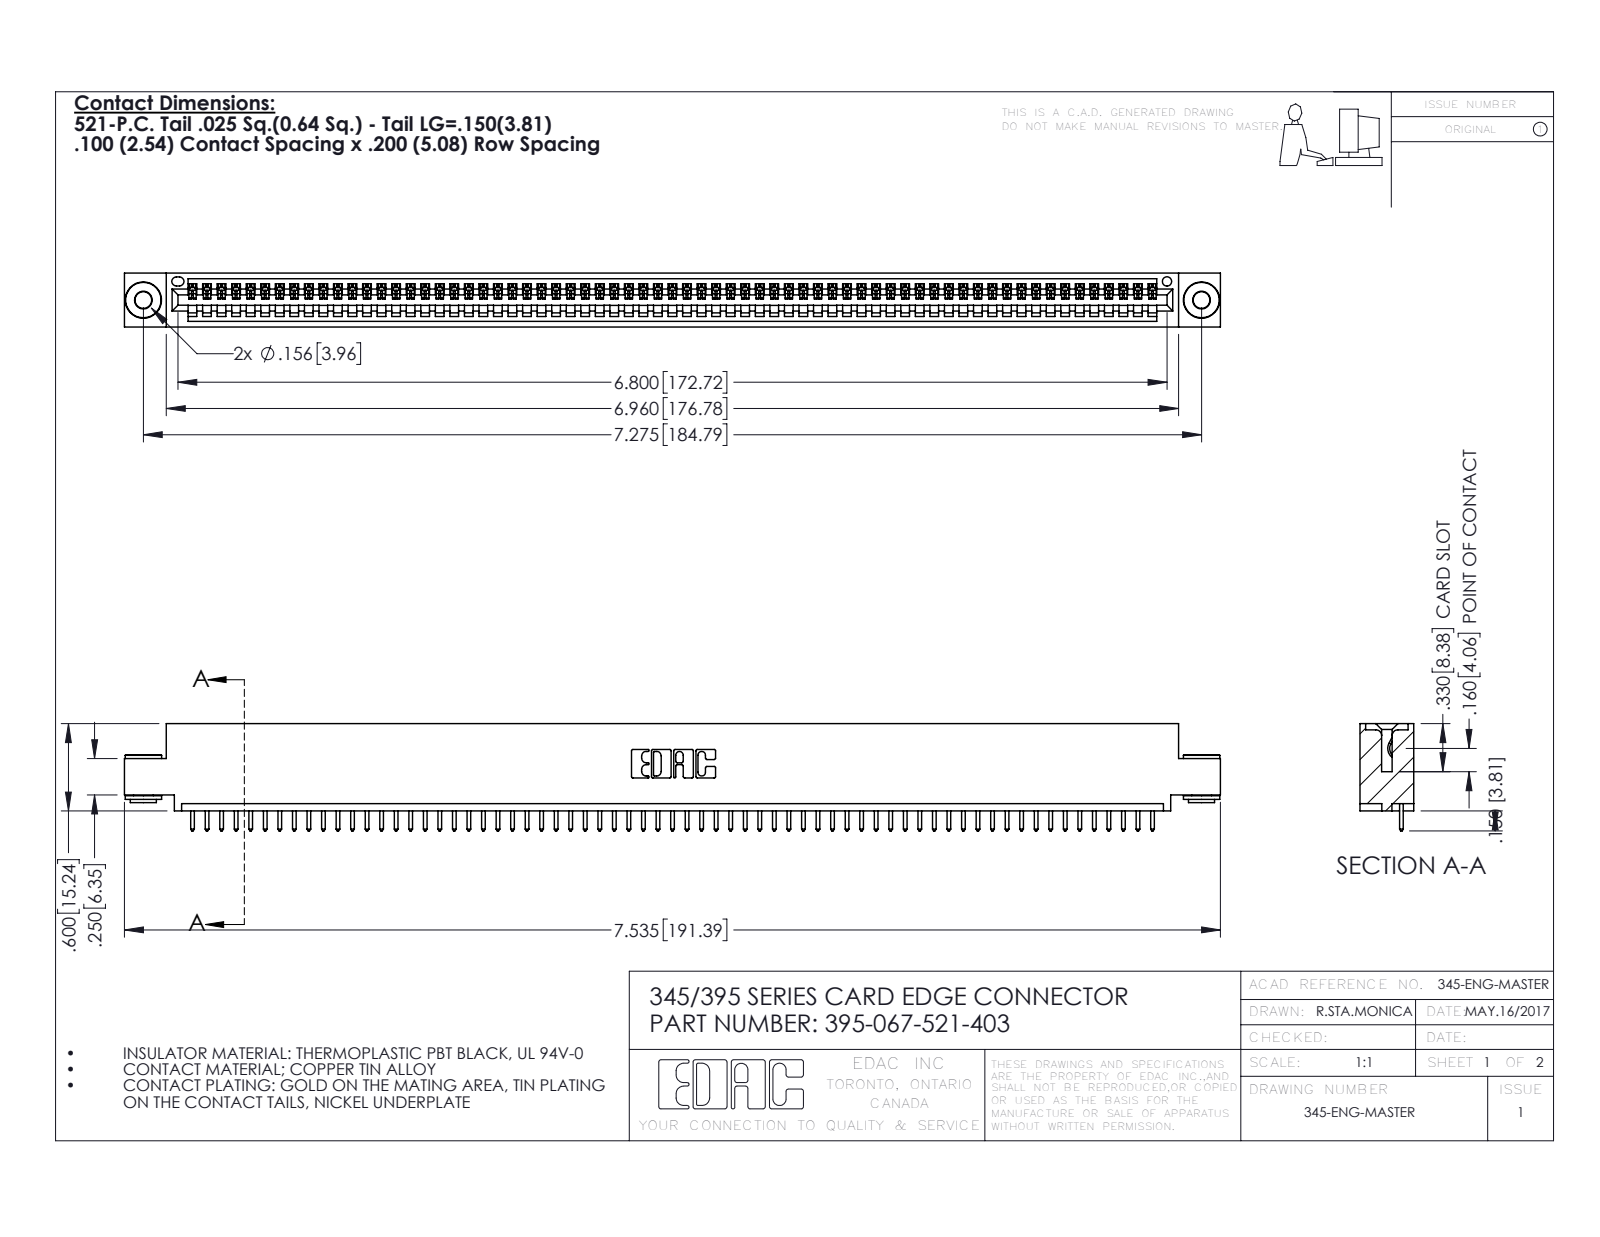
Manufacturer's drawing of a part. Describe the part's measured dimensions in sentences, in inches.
The part is named "345 Part_0.110 Offset - 0.156 Dia-TH; 345-250-002_345-250-002-102; 345-292-001_345-293-121; 395-067-521-403". Its 3-D file was written by "SolidWorks 2016 (CONFIG_CONTROL_DESIGN)". It is 70 solids with 4054 faces: 2774 planar, 1272 cylindrical and 8 other. Overall it measures 7.535 by 0.737 by 0.37 inches. Its volume is 1.107 cubic inches and its surface area 37.19 square inches. Round holes: 2 of diameter 0.116, 2 of diameter 0.156, 1 of diameter 0.064. Round bosses or shafts: 2 of diameter 0.25, 2 of diameter 0.18, 2 of diameter 0.136. Partial cylindrical surfaces (rounded edges, fillets, slot ends): 134 of radius 0.006, 134 of radius 0.01, 22 of radius 0.01, 6 of radius 0.007, 6 of radius 0.031, 3 of radius 0.026, 2 of radius 0.031, 2 of radius 0.04. The main face-to-face distances are 0.072, 0.298, 0.37, 0.2, 0.025, 0.098, 0.272, 0.225, 0.149, 0.072. The hole center spacings are 0.27, 7.039, 7.275.
